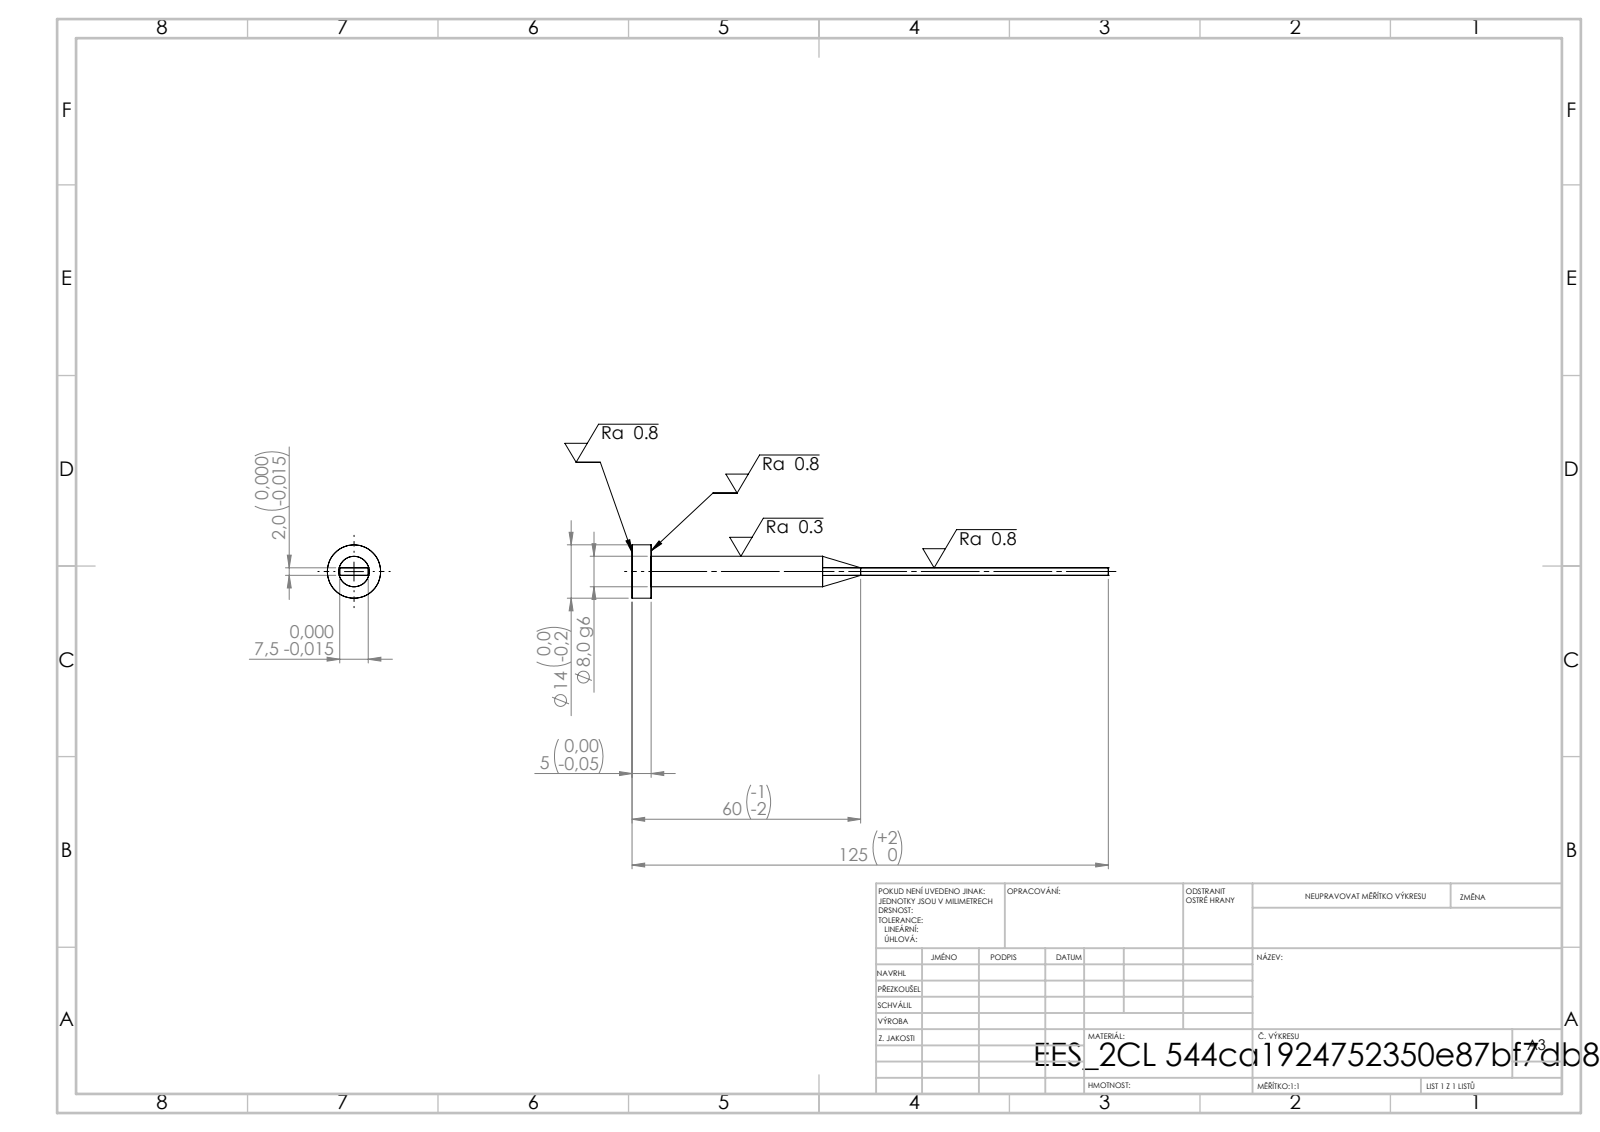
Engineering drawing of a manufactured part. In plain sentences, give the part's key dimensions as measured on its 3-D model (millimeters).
Its 3-D file was written by "SolidWorks 2019 (CONFIG_CONTROL_DESIGN)". It is 1 solid with 15 faces: 7 planar, 4 cylindrical and 4 other. Overall it measures 125 by 14 by 14 millimeters. Its volume is 4 321 cubic millimeters and its surface area 3 075 square millimeters. Round bosses or shafts: 1 of diameter 14, 1 of diameter 8. The main face-to-face distances are 2, 7.5, 5, 125, 120.
